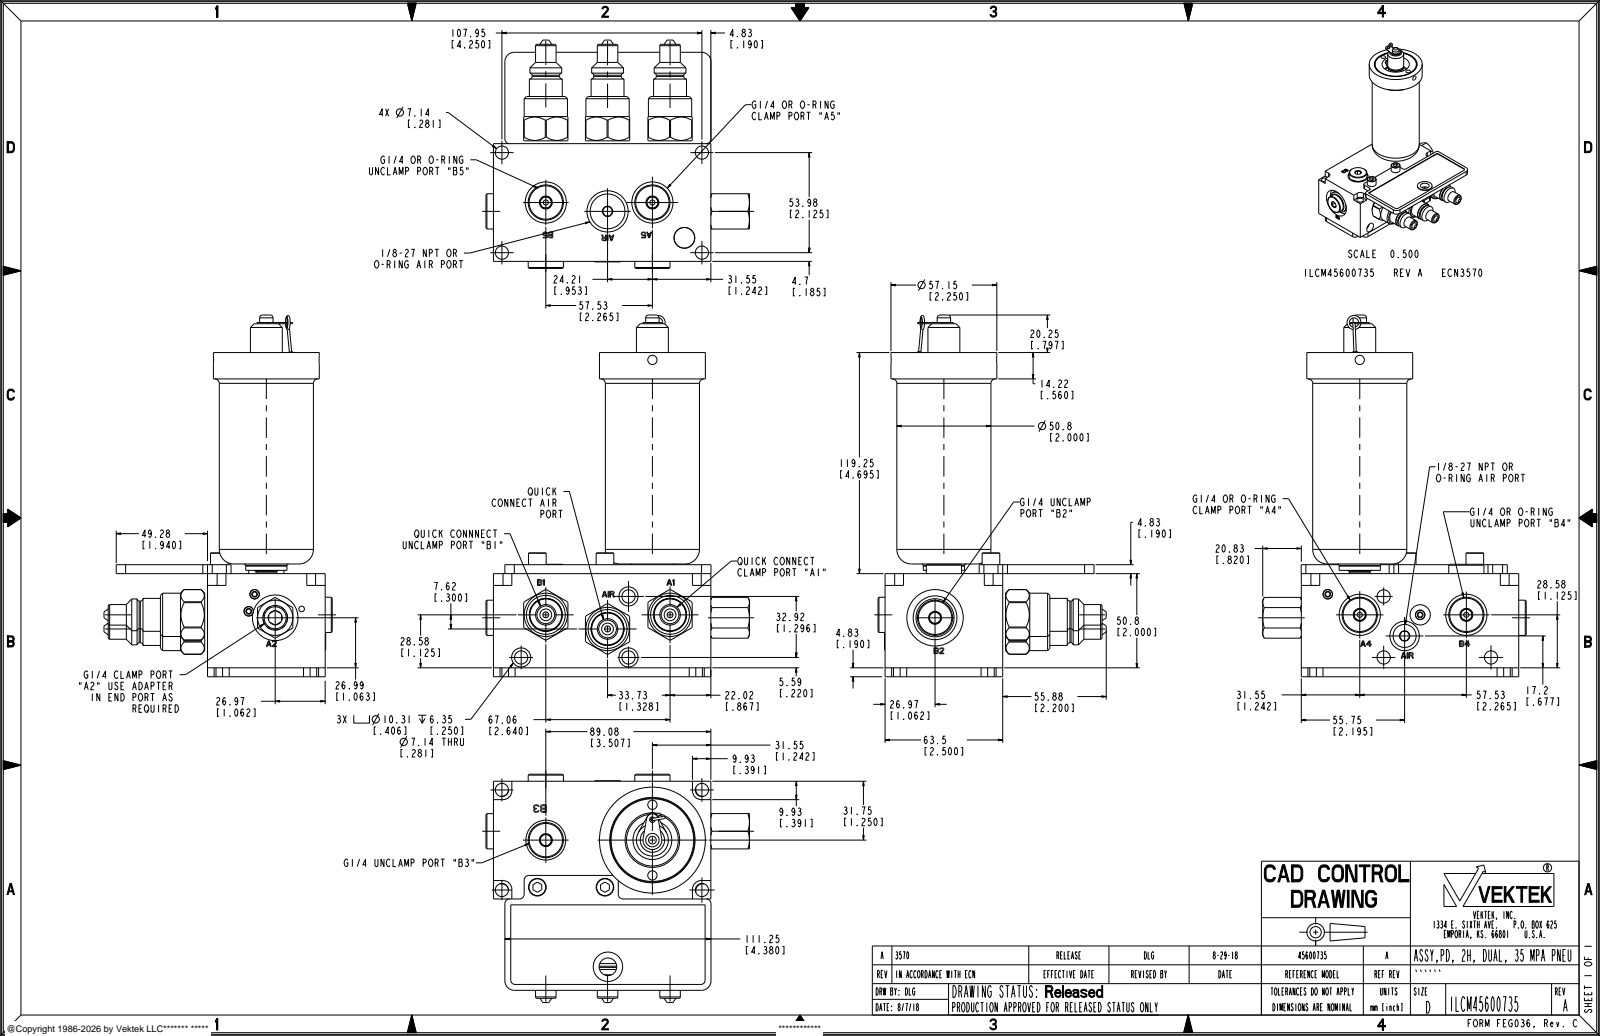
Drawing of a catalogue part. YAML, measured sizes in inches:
part_name: "ILCM45600735; 45600511; 30871966"
step_written_by: "PRO/ENGINEER BY PARAMETRIC TECHNOLOGY CORPORATION, 2013320 (CONFIG_CONTROL_DESIGN)"
units: inches
bodies: {solids: 8, faces: 1854, planar: 1094, cylindrical: 370, other: 390}
overall_size: [7.682, 5.599, 4.85]
volume: 35.9
surface_area: 213.1
round_holes:
  - {diameter: 0.281, count: 8}
  - {diameter: 0.875, count: 5}
  - {diameter: 0.123, count: 4}
  - {diameter: 0.202, count: 4}
  - {diameter: 0.197, count: 3}
  - {diameter: 0.406, count: 3}
  - {diameter: 0.514, count: 3}
  - {diameter: 0.079, count: 2}
  - {diameter: 0.118, count: 2}
  - {diameter: 0.468, count: 2}
  - {diameter: 0.846, count: 2}
  - {diameter: 1.25, count: 2}
round_bosses_or_shafts:
  - {diameter: 0.748, count: 5}
  - {diameter: 0.197, count: 4}
  - {diameter: 0.177, count: 4}
  - {diameter: 0.92, count: 3}
  - {diameter: 0.699, count: 3}
  - {diameter: 0.675, count: 3}
  - {diameter: 0.585, count: 3}
  - {diameter: 0.436, count: 3}
partial_cylinders:
  - {radius: 0.09, count: 70}
  - {radius: 0.14, count: 12}
  - {radius: 0.1, count: 6}
  - {radius: 0.187, count: 4}
  - {radius: 0.2, count: 3}
  - {radius: 0.536, count: 3}
  - {radius: 0.812, count: 2}
  - {radius: 0.108, count: 1}
face_to_face_distances: [2, 0.19, 2.19, 2.5, 0.17, 2.17, 2.36, 4.62, 0.02, 2.38]
hole_center_spacings: [0.75, 0.752, 0.972, 2.125, 2.265, 2.322, 2.386, 4.25]
